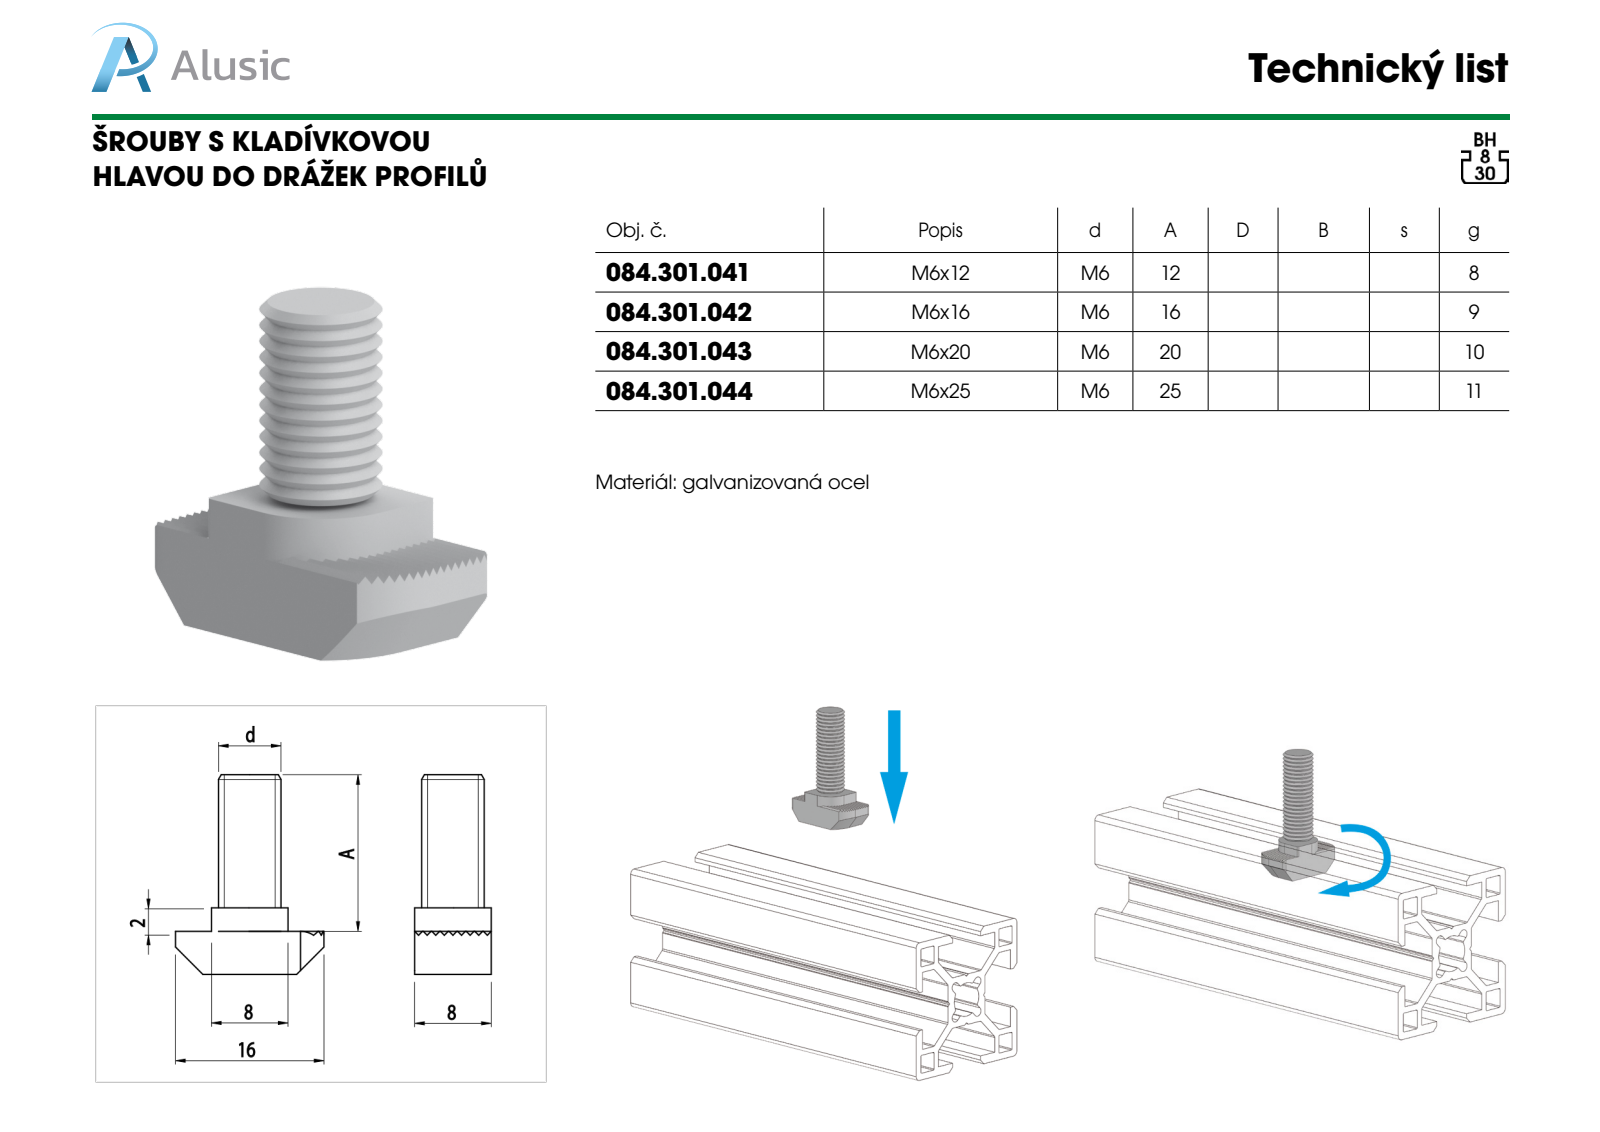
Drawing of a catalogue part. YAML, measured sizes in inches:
part_name: "084.301.042"
step_written_by: "SolidWorks 2012 (CONFIG_CONTROL_DESIGN)"
units: inches
bodies: {solids: 2, faces: 158, planar: 80, cylindrical: 8, other: 70}
overall_size: [0.811, 0.614, 0.307]
volume: 0.058
surface_area: 1.35
partial_cylinders:
  - {radius: 0.01, count: 2}
  - {radius: 0.02, count: 2}
  - {radius: 0.157, count: 2}
  - {radius: 0.197, count: 2}
face_to_face_distances: [0.307, 0.264, 0.042, 0.014, 0.028, 0.07, 0.276, 0.811, 0.547, 0.535]
